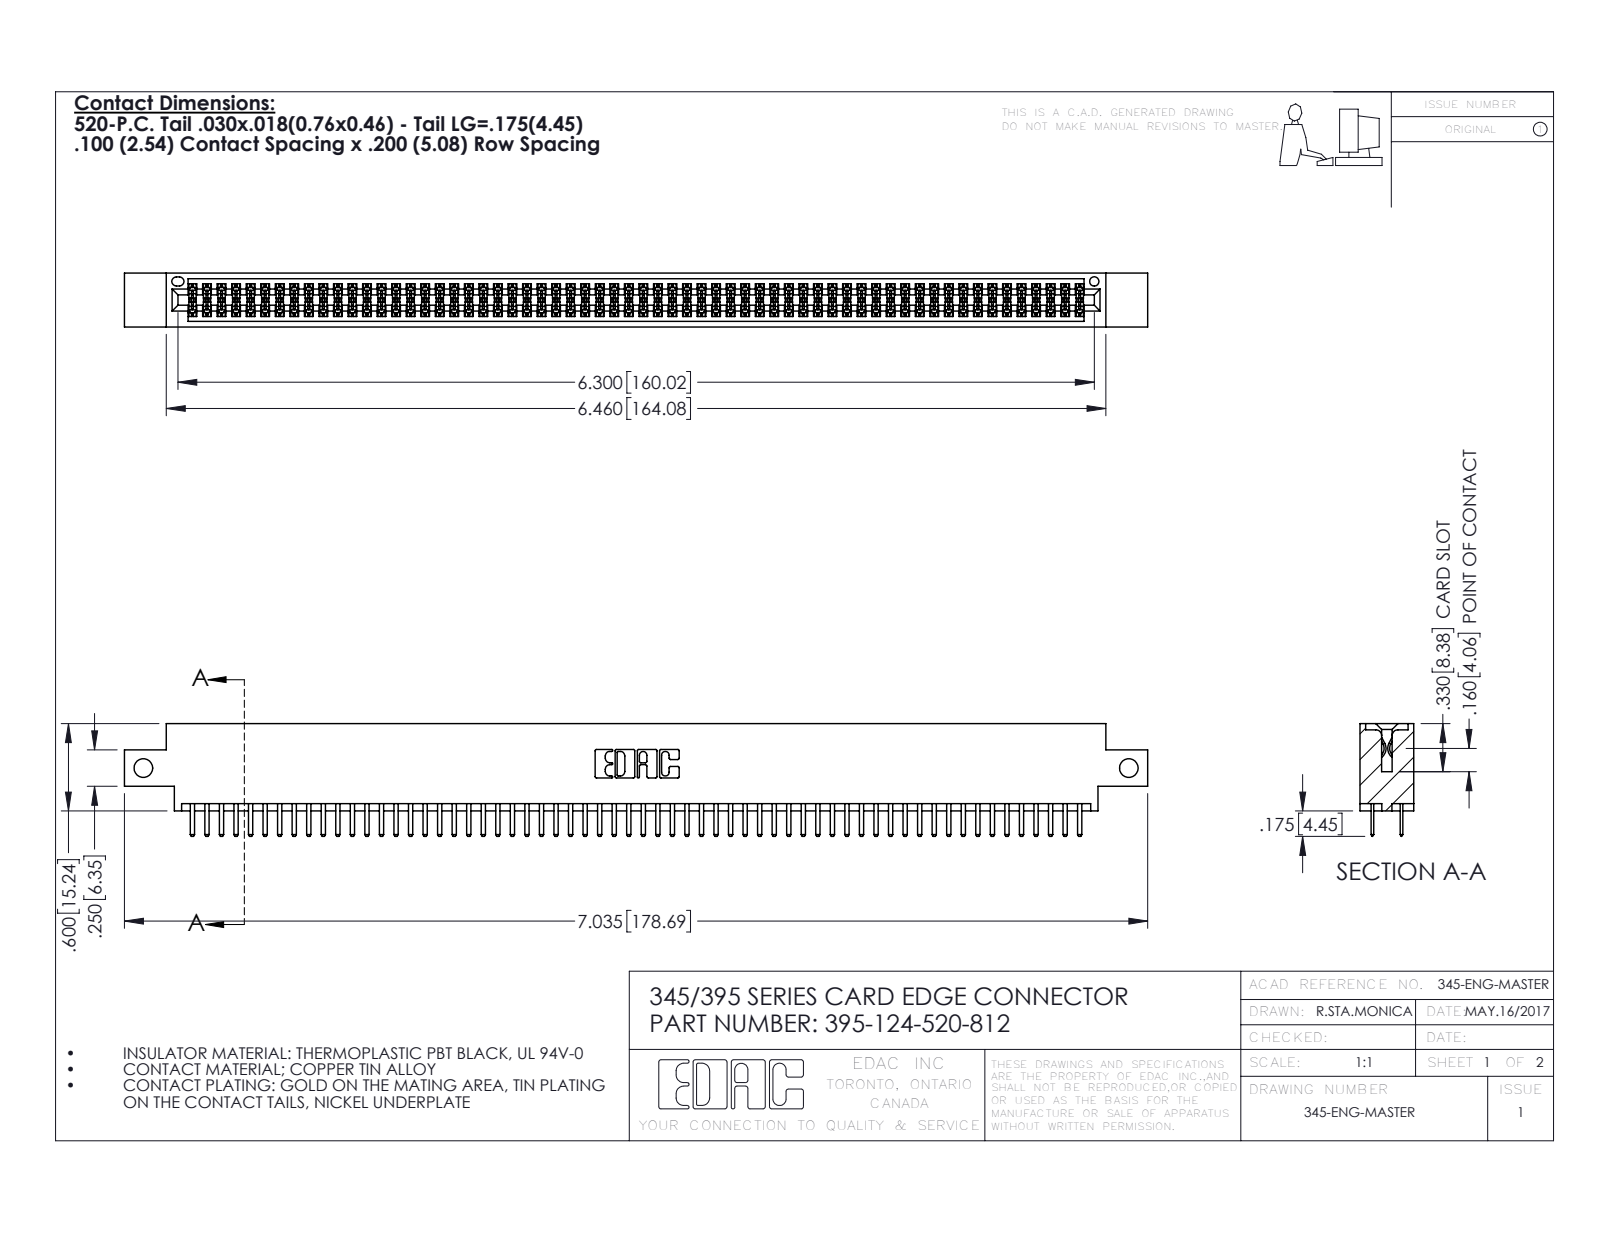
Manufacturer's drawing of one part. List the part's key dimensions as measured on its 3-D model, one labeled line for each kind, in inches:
Part name (STEP PRODUCT): 395-124-520-812; 345-292-001_345-293-120; 345 Part_0.170 Offset - Side Mount
STEP written by: SolidWorks 2016 (CONFIG_CONTROL_DESIGN)
Units: inches
Bodies: 125 solids, 6826 faces (4424 planar, 2402 cylindrical, 0 other)
Overall size (bounding box): 7.035 × 0.775 × 0.37
Volume: 1.055 in³ · Surface area: 40.04 in²
Round holes (diameter × count): ⌀0.128 ×2, ⌀0.064 ×1
Partial cylindrical surfaces — rounded edges, fillets, slot ends (radius × count): R0.006 ×186, R0.01 ×128, R0.01 ×22, R0.007 ×6, R0.031 ×6, R0.026 ×3, R0.014 ×2, R0.019 ×2
Main face-to-face distances: 0.072, 0.298, 0.2, 0.37, 0.098, 0.272, 0.025, 0.225, 0.022, 0.072
Hole centre spacings: 6.775
